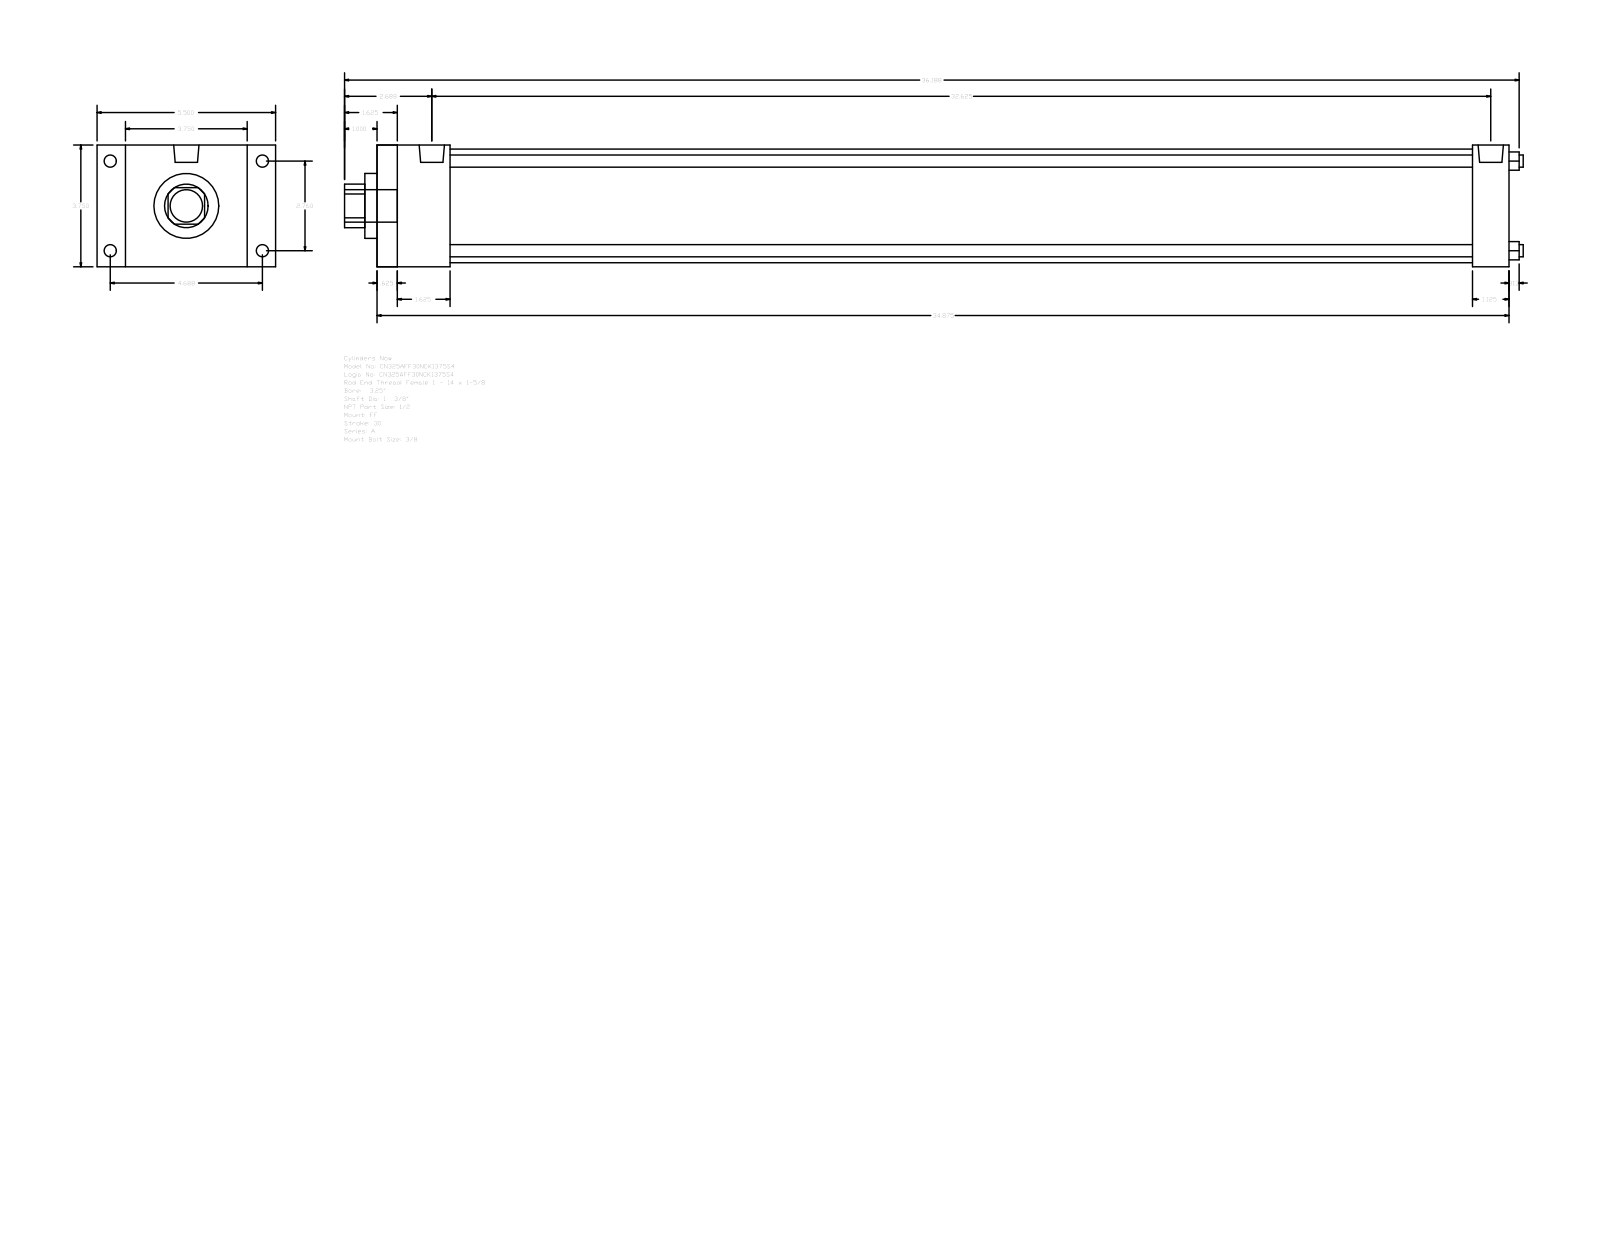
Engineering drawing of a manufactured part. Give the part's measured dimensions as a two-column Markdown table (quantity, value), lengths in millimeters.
| quantity | value |
| --- | --- |
| part name | A_FF__0325_1.375 |
| STEP written by | GSSL Pune (CONFIG_CONTROL_DESIGN) |
| units | millimeters |
| bodies | 0 solids, 92 faces (64 planar, 28 cylindrical, 0 other) |
| overall size | 922.34 × 139.7 × 95.25 |
| round holes (diameter × count) | 9.53 × 4, 34.92 × 1, 50.8 × 1, 88.9 × 1 |
| round bosses / shafts (diameter × count) | 9.53 × 4, 8.73 × 4, 19.77 × 2, 25.4 × 1 |
| partial cylindrical surfaces (radius × count) | 17.06 × 1 |
| main face-to-face distances | 95.24, 885.83, 15.87, 869.96, 28.58, 22.23, 117.47, 57.15, 857.25, 41.28 |
| hole center spacings | 49.57, 70.1, 99.14 |
